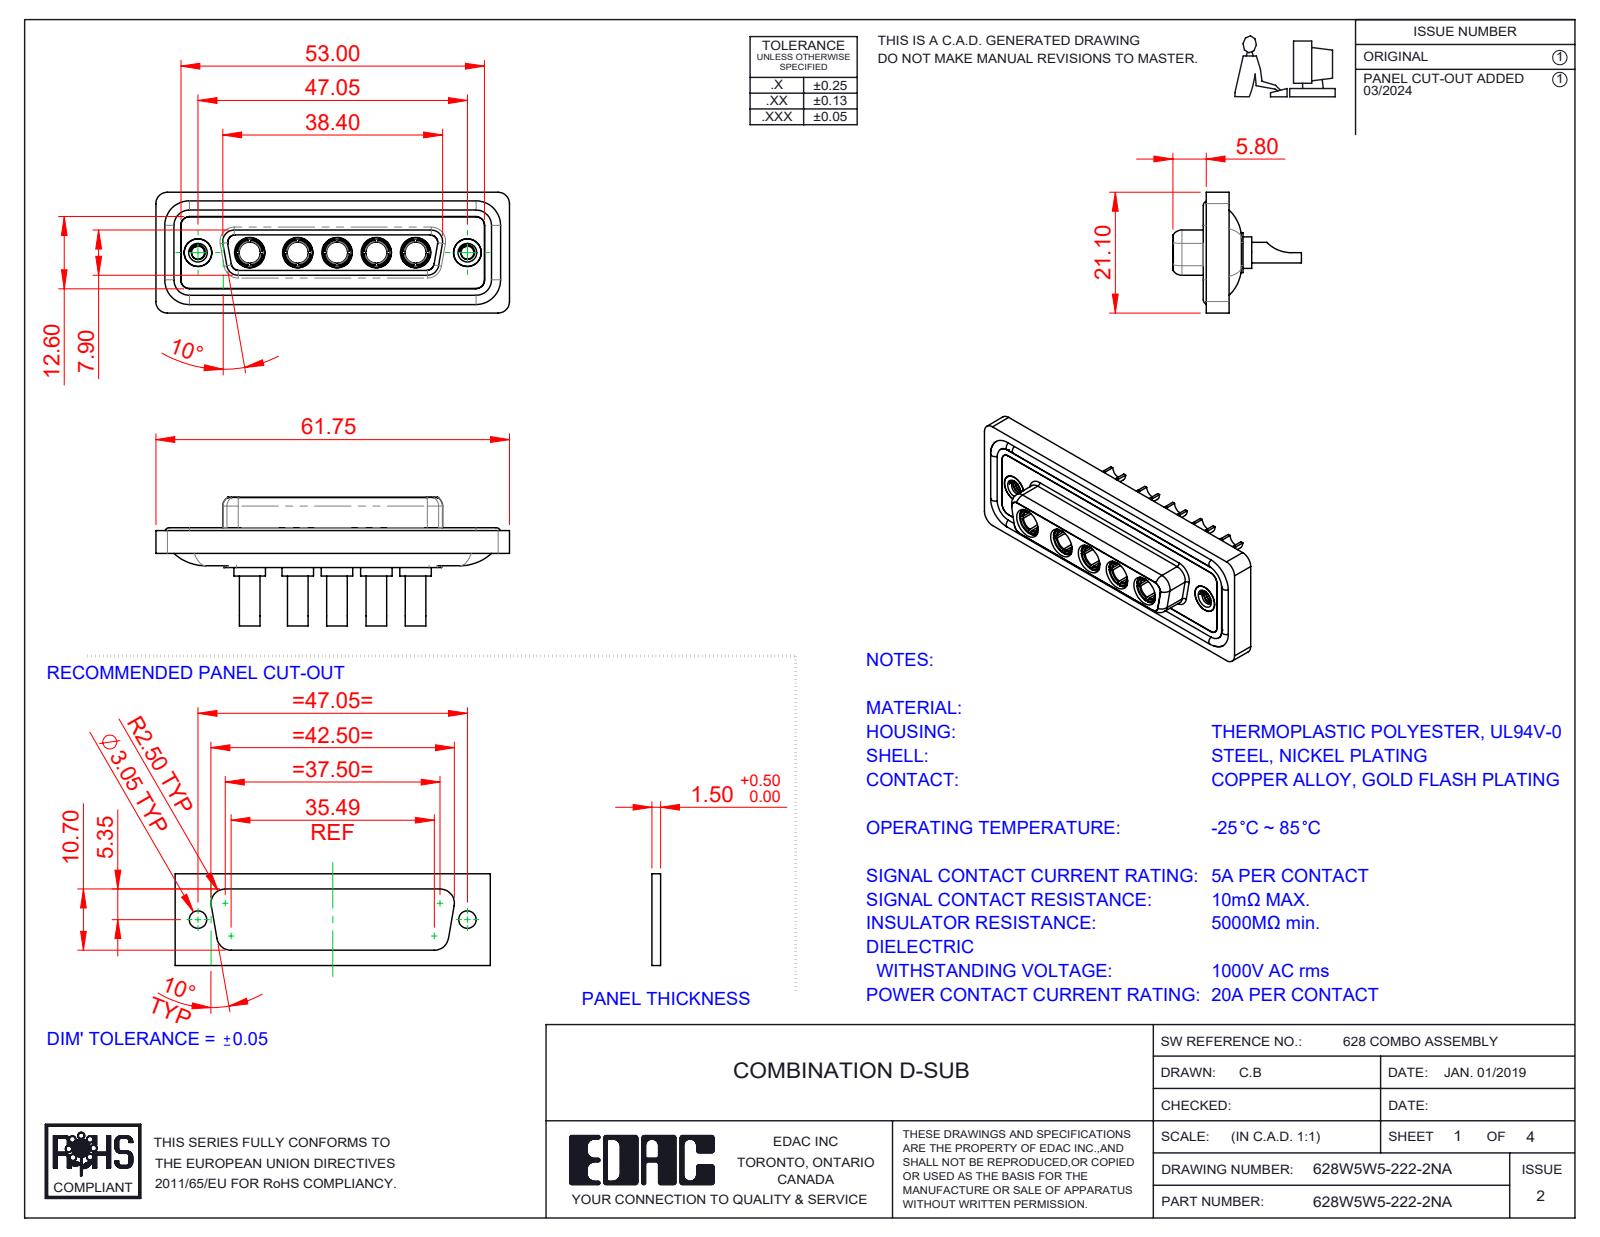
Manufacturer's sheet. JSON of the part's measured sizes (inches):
{"part_name": "628Combo Waterproof Housing_25 Contacts; 628Combo Shell Rear_25 Contacts; 628Combo Housing_5W5; 628W5W5-222-2NA (+3 more)", "step_written_by": "SolidWorks 2023 (CONFIG_CONTROL_DESIGN)", "units": "inches", "bodies": {"solids": 17, "faces": 784, "planar": 265, "cylindrical": 320, "other": 199}, "overall_size": [2.431, 0.884, 0.831], "volume_in3": 0.503, "surface_area_in2": 21.43, "round_holes": [[0.191, 7], [0.106, 5], [0.146, 5], [0.209, 5], [0.089, 2], [0.157, 2], [0.159, 2], [0.197, 2]], "round_bosses_or_shafts": [[0.217, 5], [0.205, 5], [0.195, 5], [0.187, 5], [0.148, 5], [0.142, 5], [0.063, 4], [0.195, 2]], "partial_cylinders_radius": [[0.059, 22], [0.079, 18], [0.053, 8], [0.063, 8], [0.083, 5], [0.01, 4], [0.02, 4], [0.024, 4]], "face_to_face_distances": [0.016, 0.071, 0.293, 0.222, 0.02, 0.278, 0.26, 0.063, 0.043, 0.114], "hole_center_spacings": [0.27, 0.356, 0.54, 1.496, 0.33, 0.6, 0.626, 0.686]}
